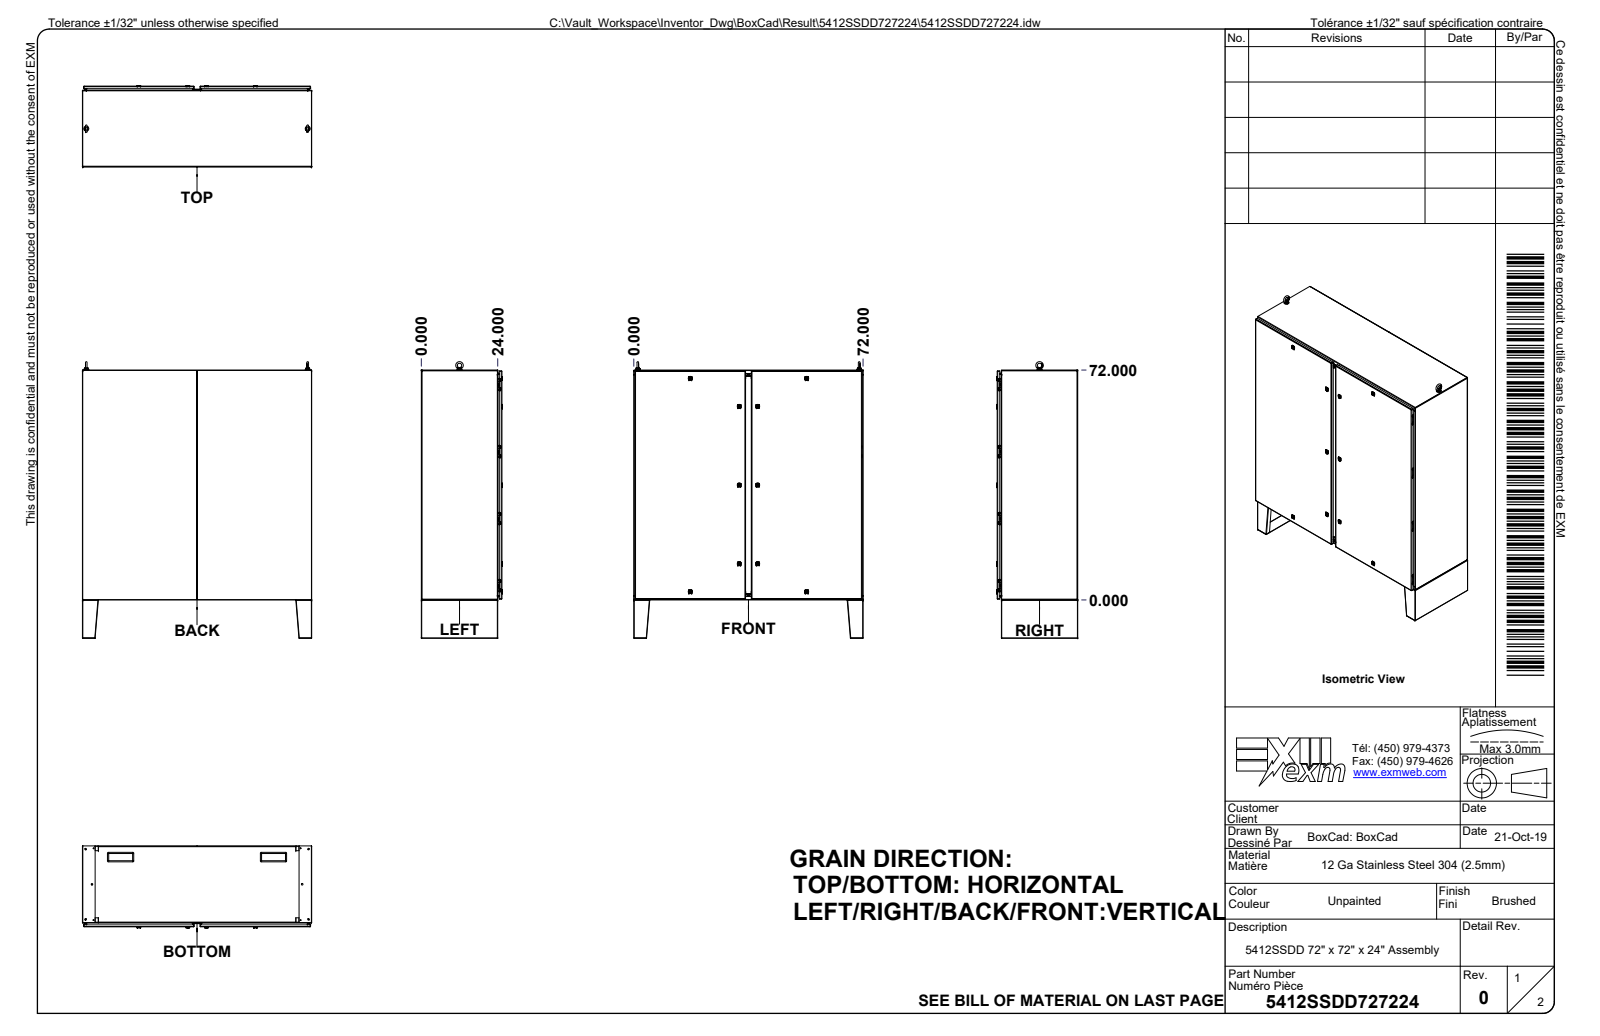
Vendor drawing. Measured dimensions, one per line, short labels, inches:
name: 5412SSDD727224; 5412SSDD727224B; 5412SSDD727224BL-P; 5412SSDD727224BR-P (+8 more)
written by: Autodesk Inventor 2024 (AUTOMOTIVE_DESIGN)
unit: in
bodies: 400 solids, 53195 faces (21112 planar, 12349 cylindrical, 19734 other)
size: 86.638 × 72 × 25.509
volume: 2 649 in³; area: 53 892 in²
holes: 368× ⌀0.177, 53× ⌀0.201, 43× ⌀0.03, 20× ⌀0.394, 17× ⌀0.315, 14× ⌀0.5, 13× ⌀0.197, 13× ⌀0.268, 12× ⌀0.118, 12× ⌀0.374, 12× ⌀0.625, 10× ⌀0.311
bosses: 252× ⌀0.249, 66× ⌀0.232, 43× ⌀0.03, 20× ⌀0.289, 20× ⌀0.177, 18× ⌀0.39, 14× ⌀0.472, 13× ⌀0.374
rounds: 1221× R0.02, 916× R0.039, 642× R0.008, 288× R0.01, 248× R0.079, 234× R0.012, 165× R0.118, 116× R0.03
face distances: 0.105, 71.895, 0.089, 25.233, 25.128, 0.105, 25.338, 25.233, 0.979, 0.874
hole spacings: 66.25, 21, 21.005, 22.083, 69.834, 0.465, 0.472, 0.492
